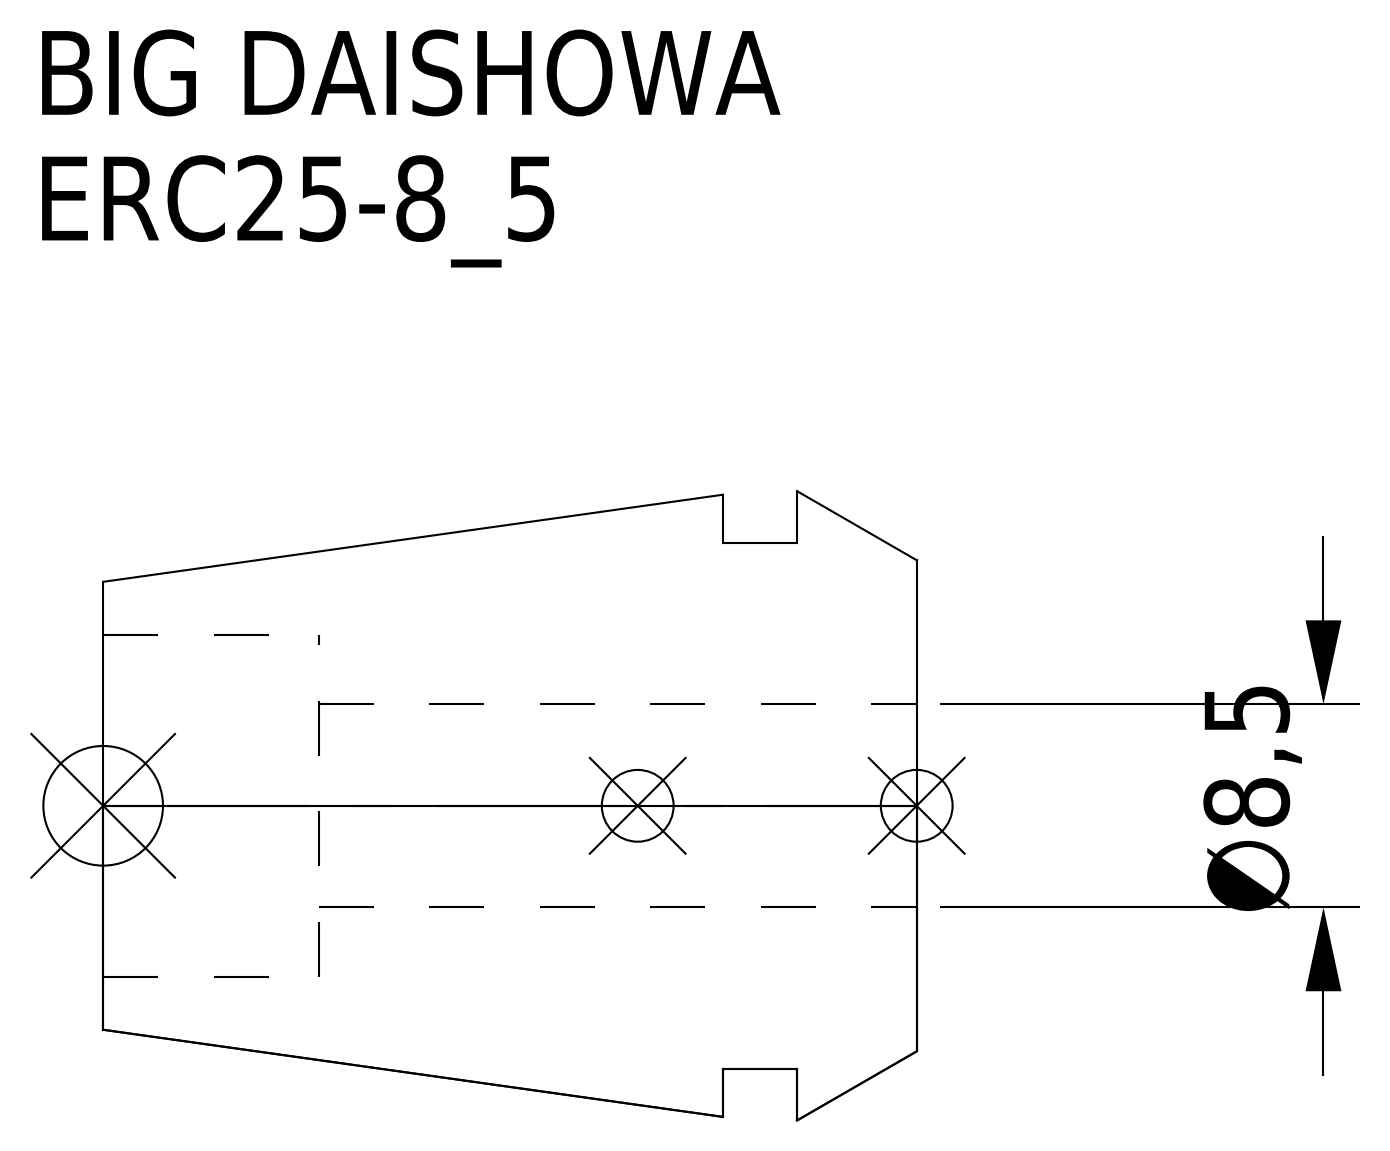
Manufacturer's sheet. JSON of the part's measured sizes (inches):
{"part_name": "ERC25-8_5", "step_written_by": "CREO PARAMETRIC BY PTC INC, 2016380 (AUTOMOTIVE_DESIGN)", "units": "inches", "bodies": {"solids": 1, "faces": 15, "planar": 5, "cylindrical": 6, "other": 4}, "overall_size": [1.339, 1.035, 1.035], "volume_in3": 0.655, "surface_area_in2": 6.75, "round_holes": [[0.335, 1], [0.563, 1]], "round_bosses_or_shafts": [[0.866, 1]], "face_to_face_distances": [0.197, 0.319, 0.122, 1.339, 1.142, 1.02, 0.984, 0.787, 0.665, 0.354]}
